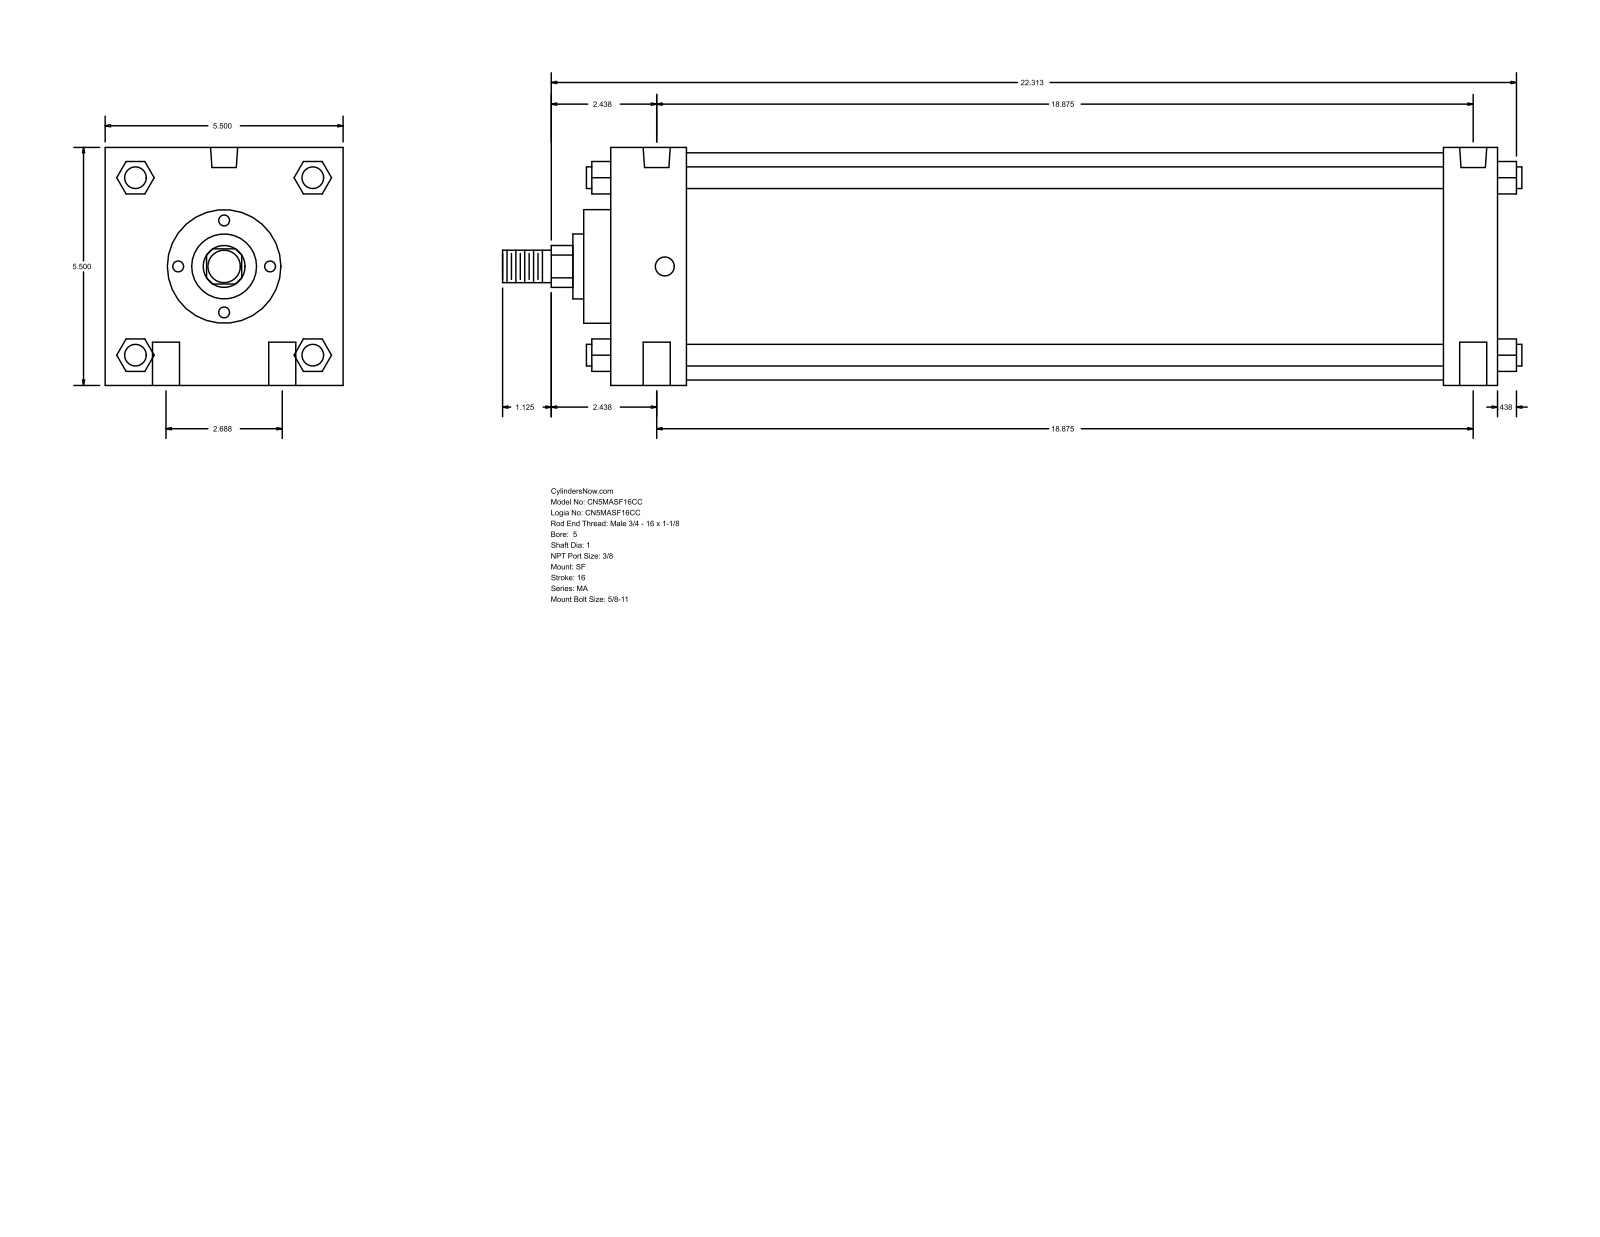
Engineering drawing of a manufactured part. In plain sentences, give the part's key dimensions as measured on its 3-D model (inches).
The part is named "MA_SF__0500_1". Its 3-D file was written by "GSSL Pune (CONFIG_CONTROL_DESIGN)". It is 0 solids with 126 faces: 95 planar, 31 cylindrical and 0 other. Overall it measures 23.563 by 5.5 by 5.5 inches. Round holes: 4 of diameter 0.625, 2 of diameter 0.437, 2 of diameter 0.627. Round bosses or shafts: 4 of diameter 0.5, 1 of diameter 5.25, 1 of diameter 2.625, 1 of diameter 1.5, 1 of diameter 1, 1 of diameter 0.75. Partial cylindrical surfaces (rounded edges, fillets, slot ends): 1 of radius 0.484. The main face-to-face distances are 5.5, 20.5, 1.75, 19.25, 17.5, 18.75, 1.25, 0.625, 2.375, 19.875. The hole center spacings are 1.344, 18.923, 18.875, 2.687, 19.065, 18.5.
